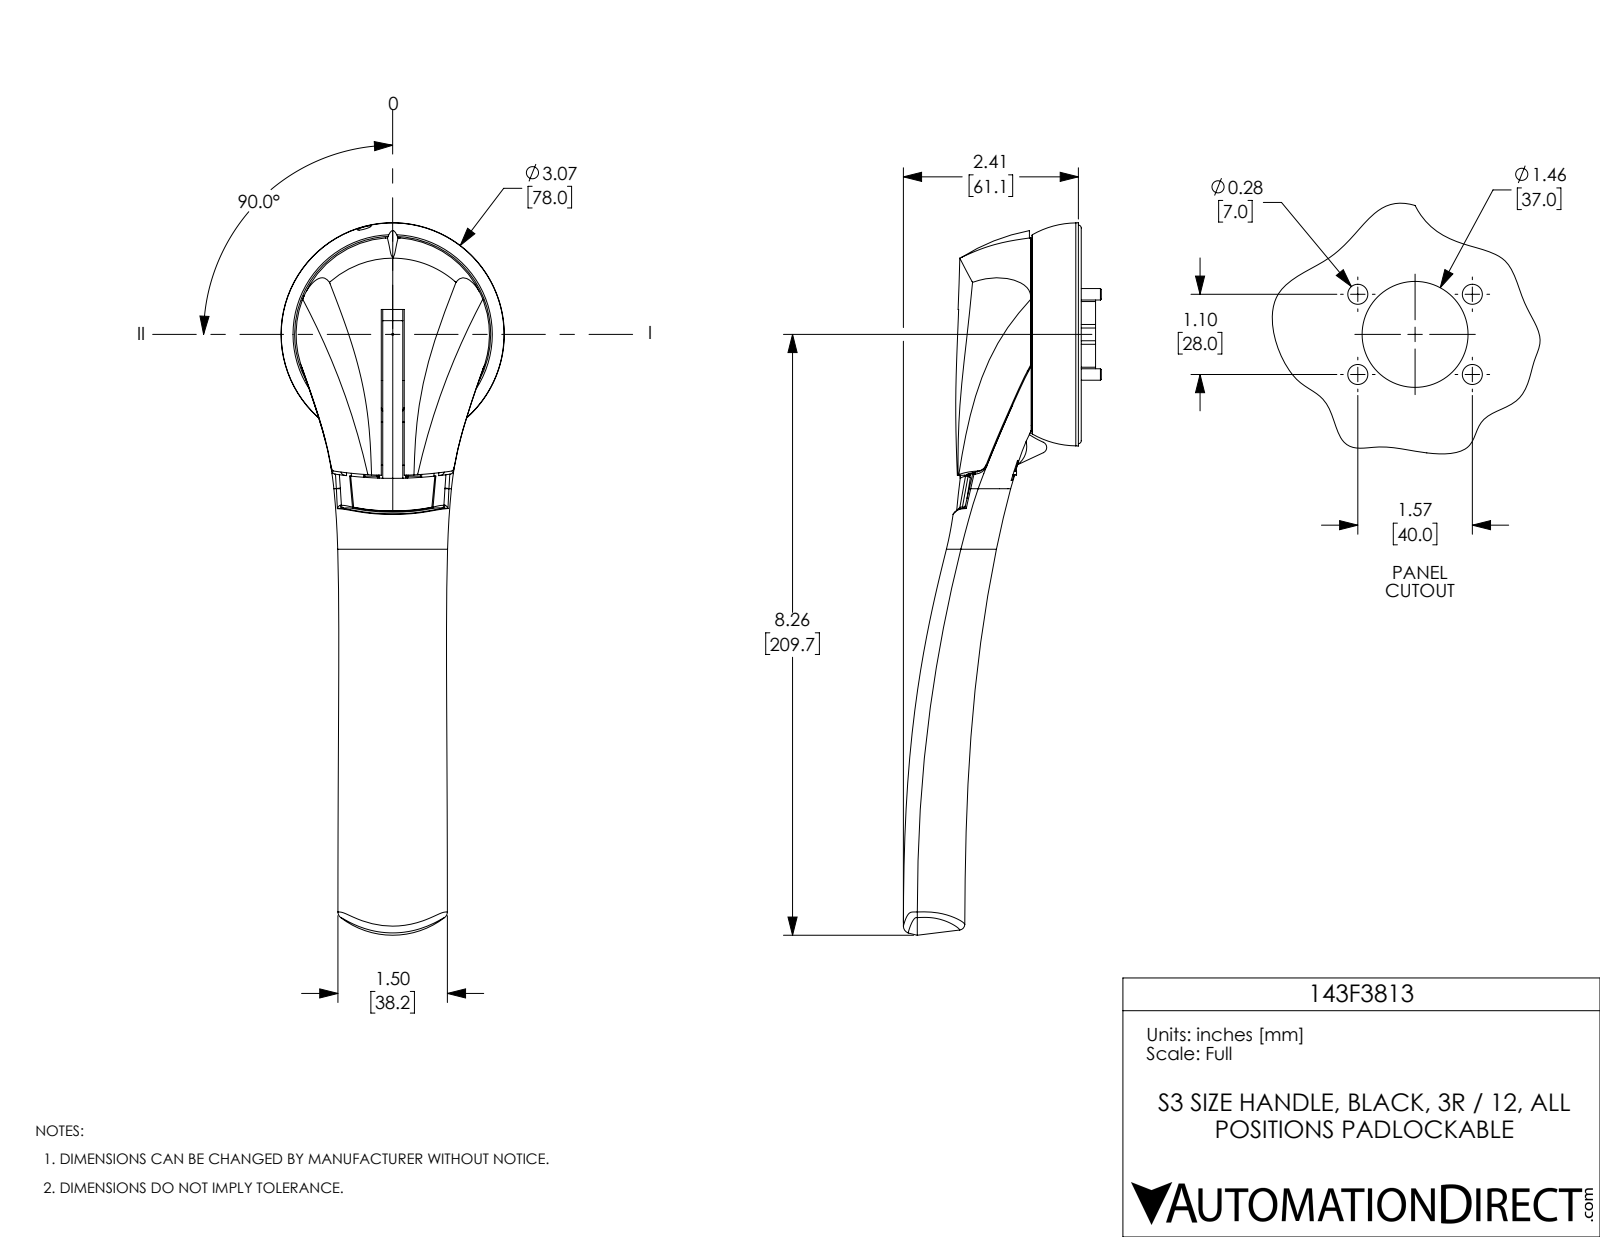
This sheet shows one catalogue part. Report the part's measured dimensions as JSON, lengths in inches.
{"part_name": "143F3813", "step_written_by": "SolidWorks 2017 (AUTOMOTIVE_DESIGN)", "units": "inches", "bodies": {"solids": 8, "faces": 1514, "planar": 806, "cylindrical": 544, "other": 164}, "overall_size": [9.793, 3.07, 2.721], "volume_in3": 12.91, "surface_area_in2": 100.4, "round_holes": [[0.157, 6], [0.339, 4], [0.425, 4], [0.03, 3], [0.169, 2], [0.362, 2], [0.118, 1], [0.189, 1], [2.992, 1]], "round_bosses_or_shafts": [[0.02, 11], [0.335, 4], [0.315, 4], [0.089, 3], [0.069, 3], [0.228, 2], [2.819, 1], [2.701, 1]], "partial_cylinders_radius": [[0.01, 221], [0.015, 20], [0.034, 20], [0.03, 15], [0.039, 4], [0.025, 3], [5.437, 3], [0.079, 2]], "face_to_face_distances": [0.024, 0.701, 0.713, 0.689, 0.035, 0.276, 0.102, 0.173, 0.244, 0.047], "hole_center_spacings": [0.961, 0.309, 0.669, 1.098, 1.102, 1.203, 1.575, 1.881]}
